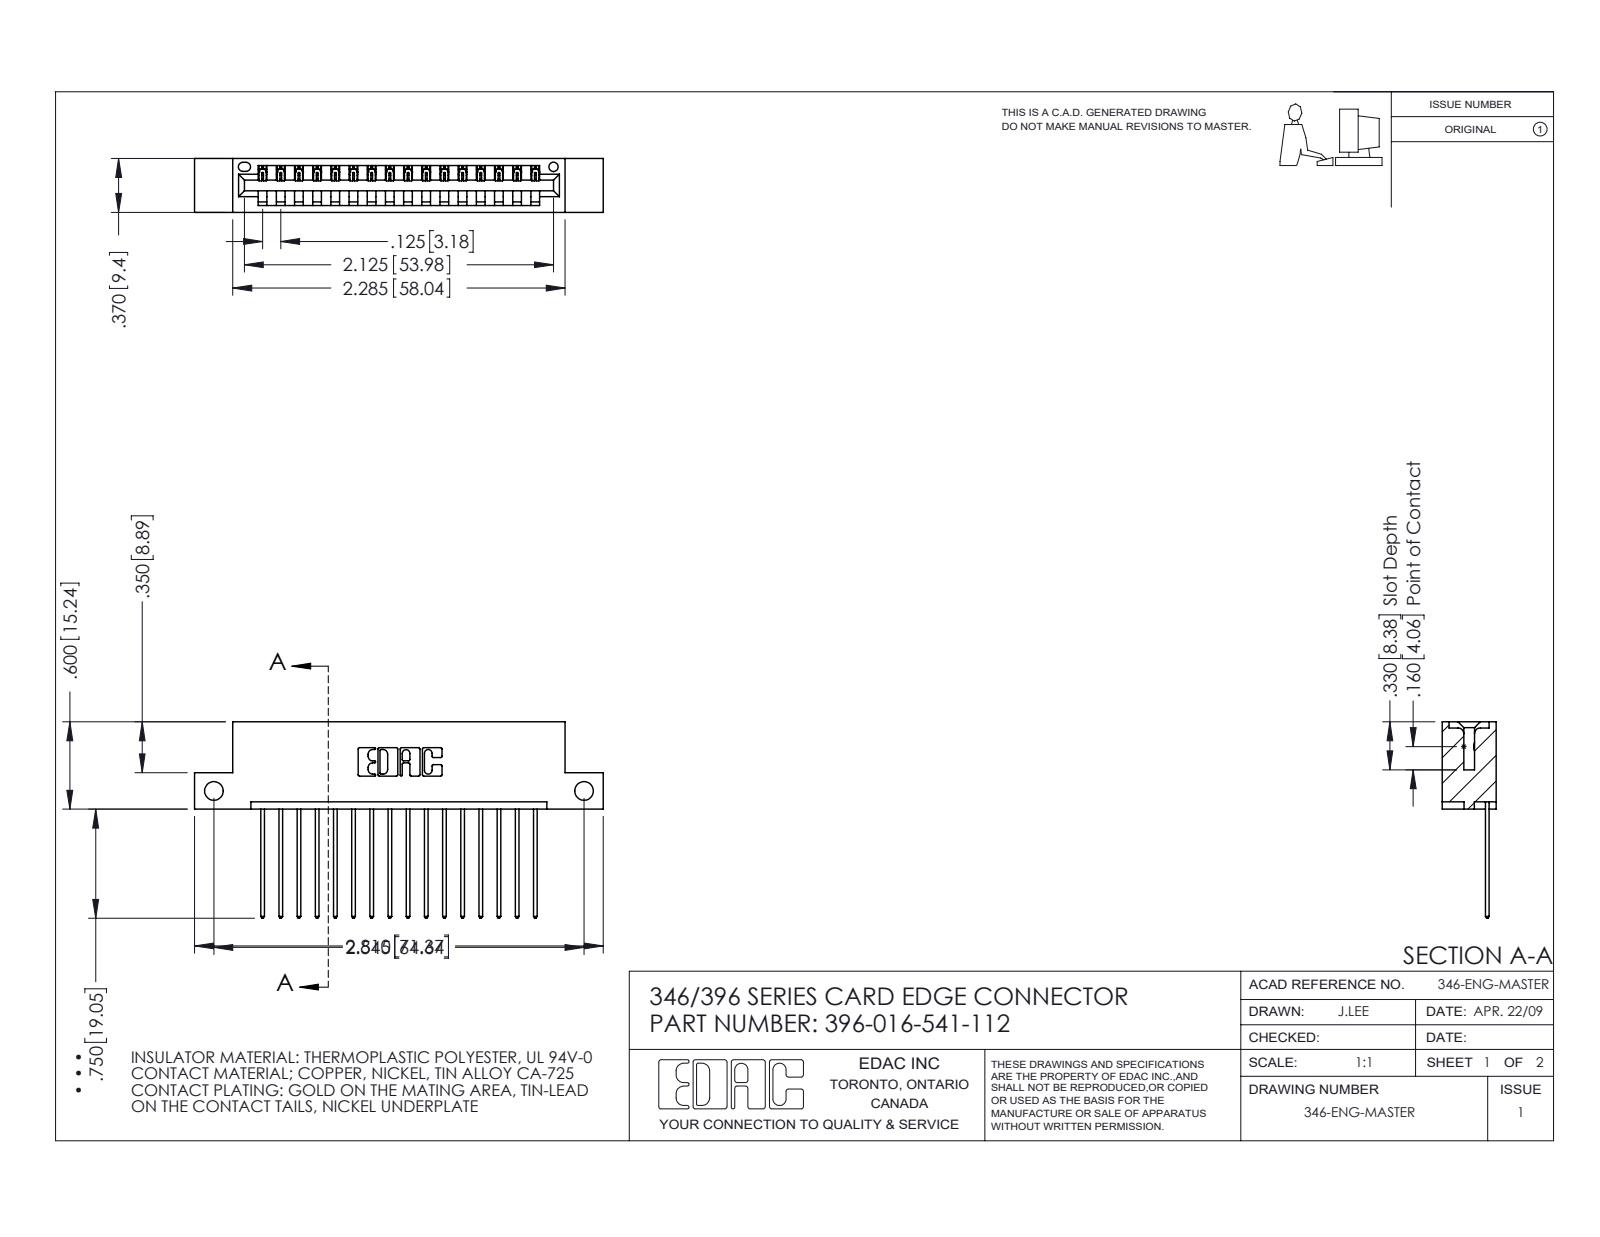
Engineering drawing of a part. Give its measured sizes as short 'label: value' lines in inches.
name: 346 Part_Flush Mounting Lugs - Side Mount; 396-016-541-112; 345-292-001_345-293-141
written by: SolidWorks 2016 (CONFIG_CONTROL_DESIGN)
unit: in
bodies: 17 solids, 1050 faces (716 planar, 334 cylindrical, 0 other)
size: 2.81 × 1.35 × 0.37
volume: 0.404 in³; area: 12.65 in²
holes: 2× ⌀0.128, 1× ⌀0.064
rounds: 32× R0.006, 32× R0.01, 22× R0.01, 6× R0.007, 6× R0.031, 3× R0.026, 2× R0.031, 2× R0.04
face distances: 0.048, 0.322, 0.25, 0.37, 0.072, 0.298, 0.025, 0.148, 0.222, 0.1
hole spacings: 2.545
